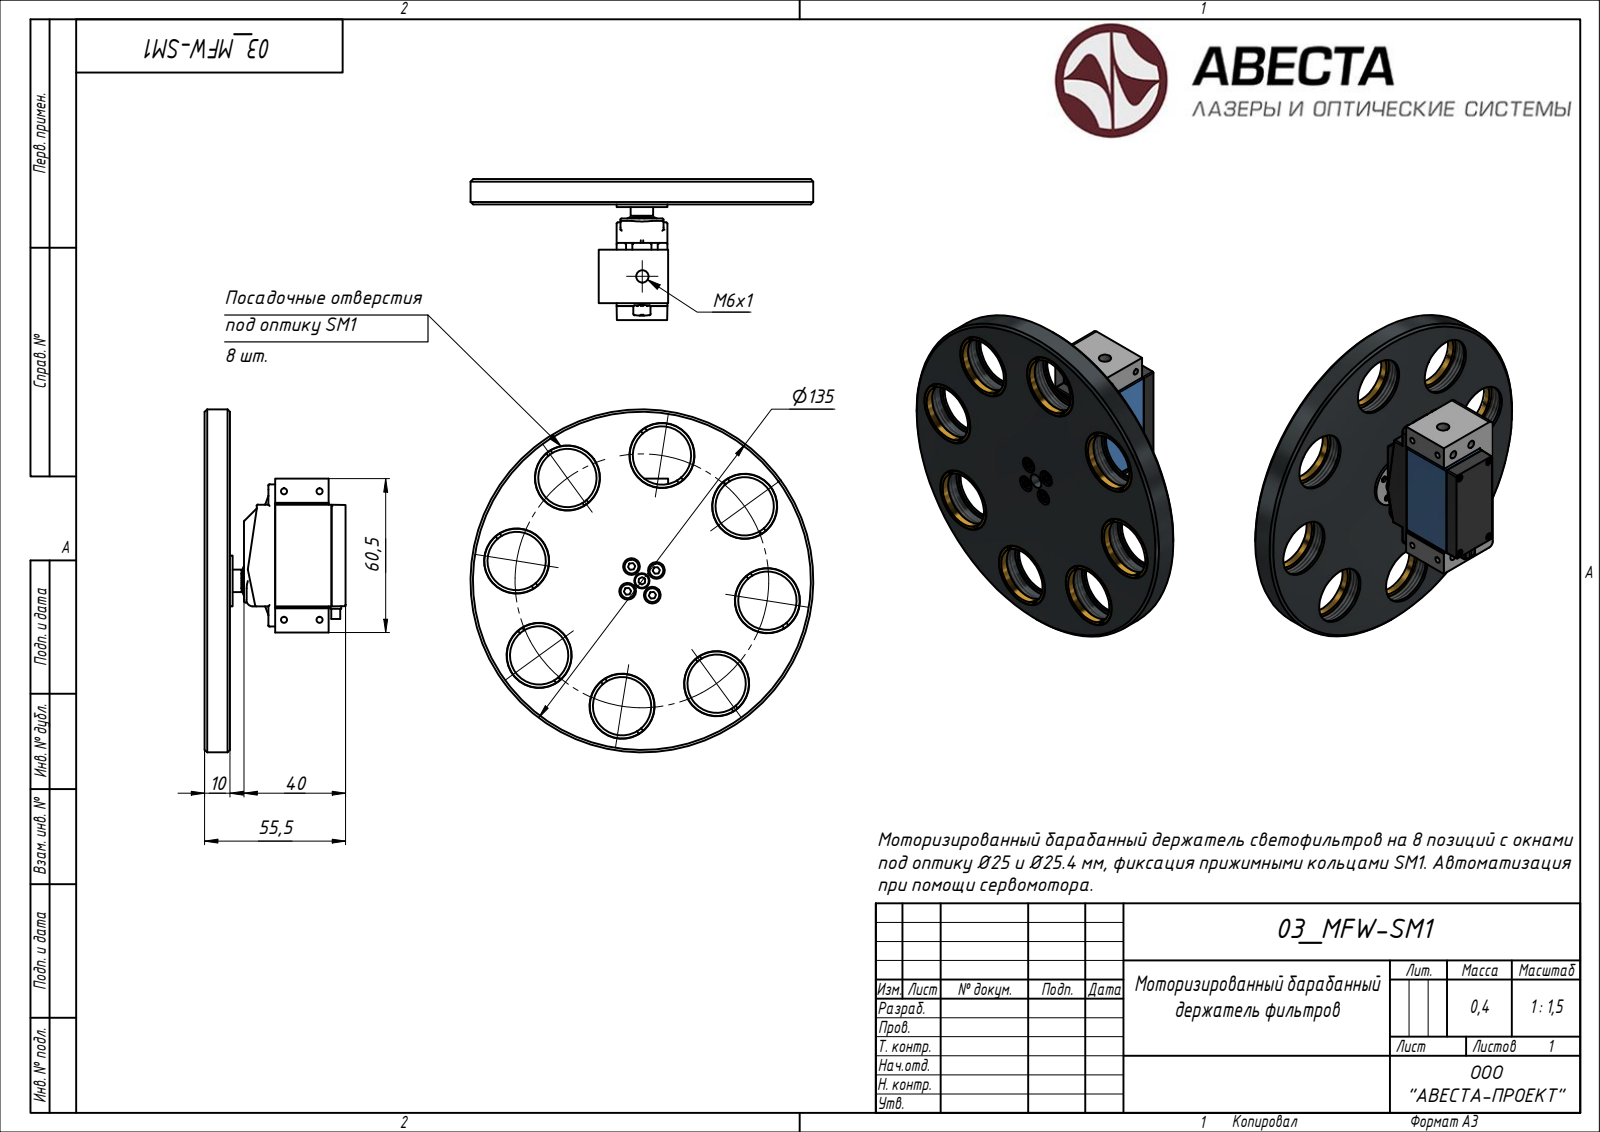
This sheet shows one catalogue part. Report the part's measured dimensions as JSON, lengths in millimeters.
{"step_written_by": "Rhino 7.34 (AUTOMOTIVE_DESIGN)", "units": "millimeters", "bodies": {"solids": 9, "faces": 998, "planar": 391, "cylindrical": 407, "other": 200}, "overall_size": [135, 135, 55.5], "volume_mm3": 152304, "surface_area_mm2": 53221, "round_holes": [[2.46, 10], [23, 8], [25.68, 8], [2.8, 4], [3.24, 4], [3.4, 4], [5, 4], [6.5, 4], [2.46, 3], [4.92, 1], [6, 1]], "round_bosses_or_shafts": [[25.4, 8], [5.5, 5], [3, 4], [135, 1], [20, 1], [8.9, 1]], "partial_cylinders_radius": [[6, 50], [0.5, 43], [0.25, 16], [0.15, 14], [0.1, 8], [12, 8], [2, 6], [1.23, 1]], "face_to_face_distances": [10, 7, 20, 1, 27, 9, 6, 3, 38.8, 39.8], "hole_center_spacings": [45.32, 50, 50.49, 55.17, 70.71, 92.39, 6.99, 7.16]}
